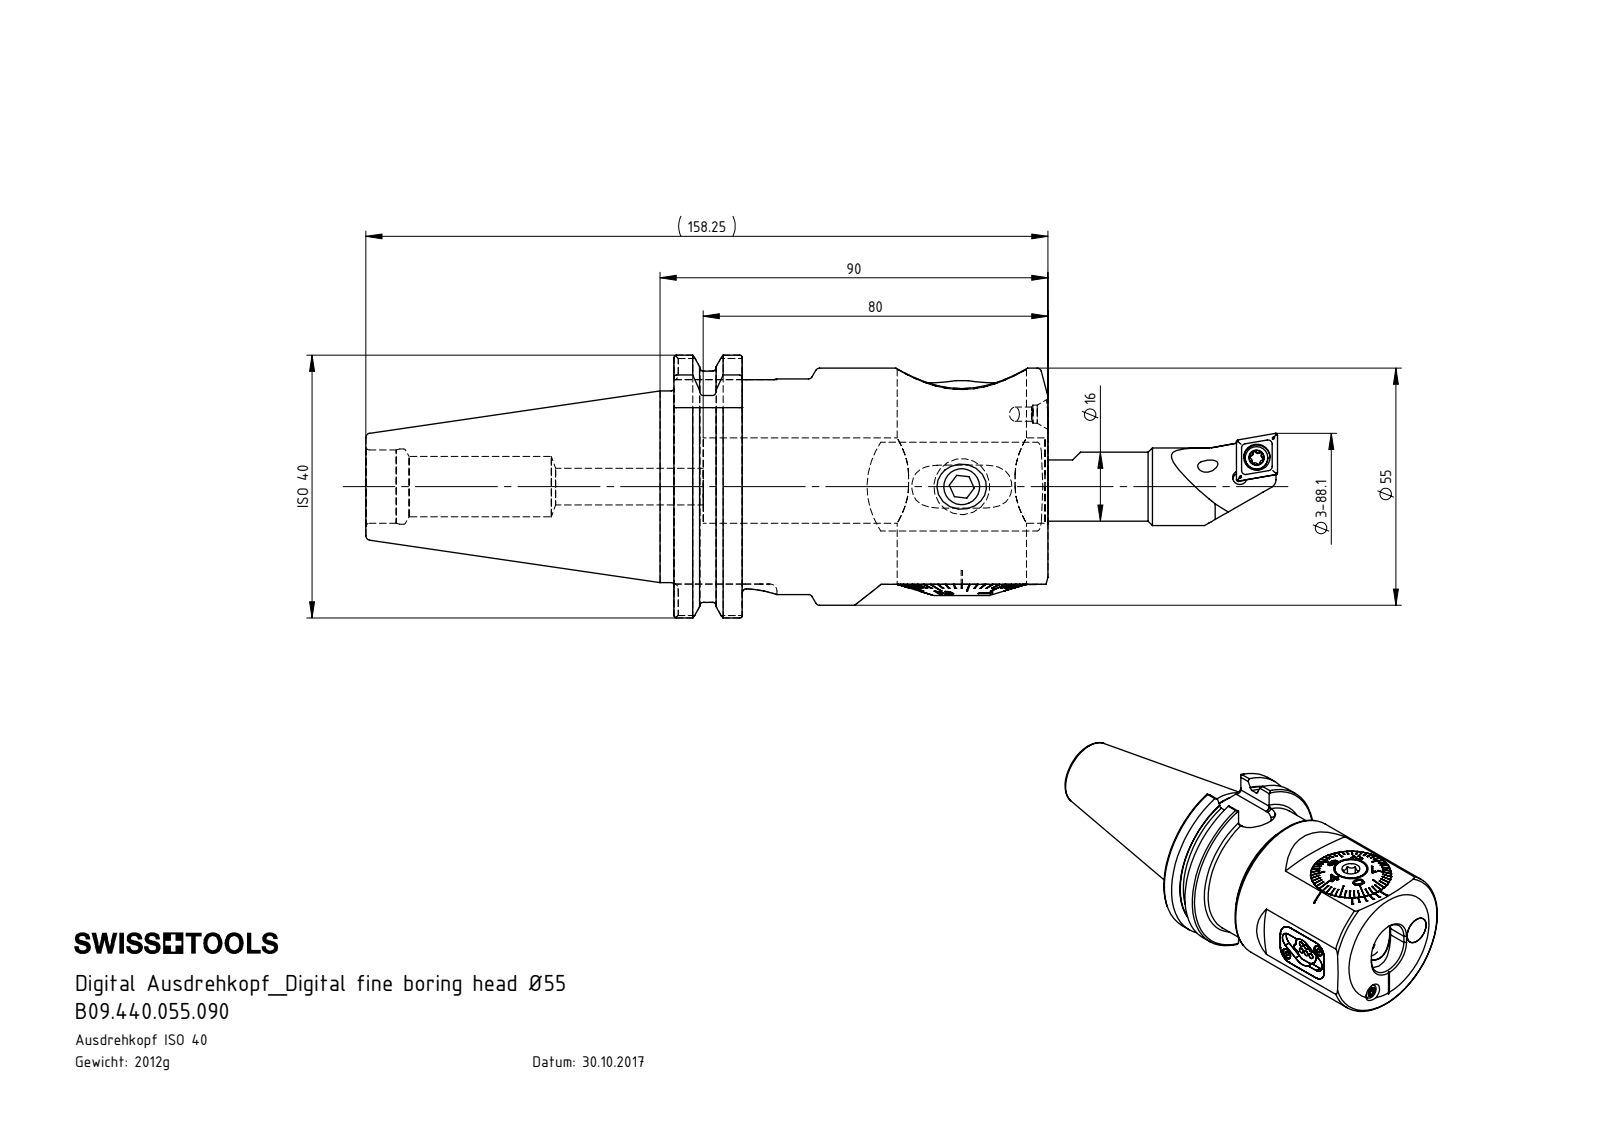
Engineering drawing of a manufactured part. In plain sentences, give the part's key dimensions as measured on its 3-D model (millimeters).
The part is named "ISO 4026 - M10 x 16_PreviewCfg; A55-BG2.011.016_D; A55-BG2.014.007_A; A55-BG2.015.007_A (+8 more)". Its 3-D file was written by "SolidWorks 2017 (CONFIG_CONTROL_DESIGN)". It is 29 solids with 1284 faces: 544 planar, 339 cylindrical and 401 other. Overall it measures 211.5 by 63.5 by 60.94 millimeters. Its volume is 257 610 cubic millimeters and its surface area 67 677 square millimeters. Round holes: 4 of diameter 3.2, 4 of diameter 8.5, 3 of diameter 1.6, 3 of diameter 3.3, 3 of diameter 4.2, 2 of diameter 2.2, 2 of diameter 3, 2 of diameter 14, 1 of diameter 4.4, 1 of diameter 6.1, 1 of diameter 8, 1 of diameter 10. Round bosses or shafts: 6 of diameter 1.9, 3 of diameter 10, 2 of diameter 18, 2 of diameter 5.25, 2 of diameter 4, 2 of diameter 3.8, 2 of diameter 2, 1 of diameter 55. Partial cylindrical surfaces (rounded edges, fillets, slot ends): 12 of radius 0.34, 12 of radius 0.59, 9 of radius 1.1, 8 of radius 1.2, 8 of radius 1.6, 5 of radius 4.5, 3 of radius 3.2, 3 of radius 4.4. The main face-to-face distances are 86.8, 3.7, 15.85, 70.95, 6.8, 2, 28.85, 4, 0.45, 5.3. The hole center spacings are 4.1, 4.32, 7.25, 8.45, 9.52, 12, 12.68, 14.5.
